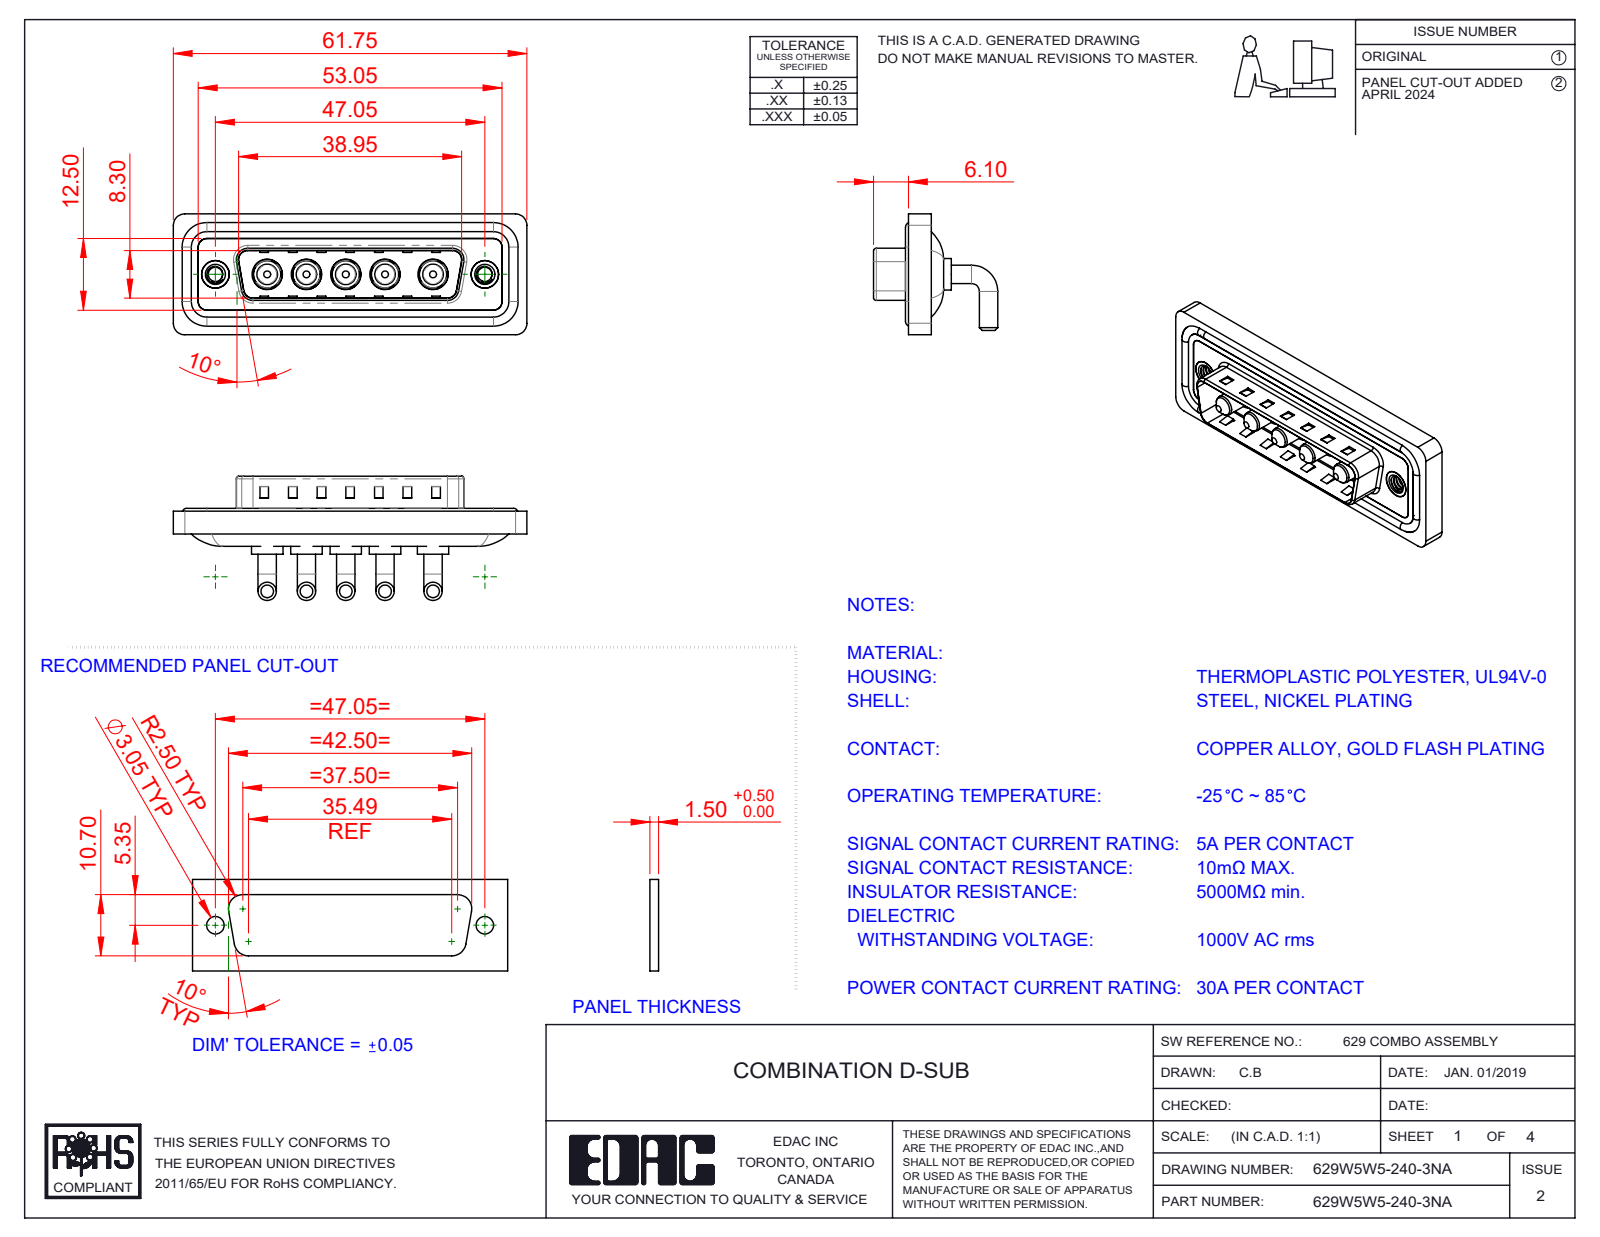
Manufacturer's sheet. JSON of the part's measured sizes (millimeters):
{"part_name": "629Combo Waterproof Housing_25 Contacts; 629Combo Shell Front_25 Contacts; Power Pin_30A RA; 629Combo Housing_5W5 (+3 more)", "step_written_by": "SolidWorks 2023 (CONFIG_CONTROL_DESIGN)", "units": "millimeters", "bodies": {"solids": 17, "faces": 692, "planar": 259, "cylindrical": 291, "other": 142}, "overall_size": [61.75, 21.7, 21.1], "volume_mm3": 7946, "surface_area_mm2": 12368, "round_holes": [[4.85, 5], [5.3, 5], [2.5, 2], [4, 2], [4.8, 2], [5, 2]], "round_bosses_or_shafts": [[3.2, 10], [5.5, 5], [5.2, 5], [4.75, 5], [3.75, 5], [3.6, 5], [1.6, 4], [4.9, 2]], "partial_cylinders_radius": [[1.5, 18], [2, 18], [0.5, 8], [1.6, 8], [2.1, 5], [0.25, 4], [0.6, 4], [0.65, 4]], "face_to_face_distances": [0.4, 2.9, 0.8, 4.5, 4.1, 1.1, 2.1, 3.1, 6, 1.5], "hole_center_spacings": [6.86, 13.73, 6.85, 6.87, 8.37, 8.38, 9.04, 9.05]}
